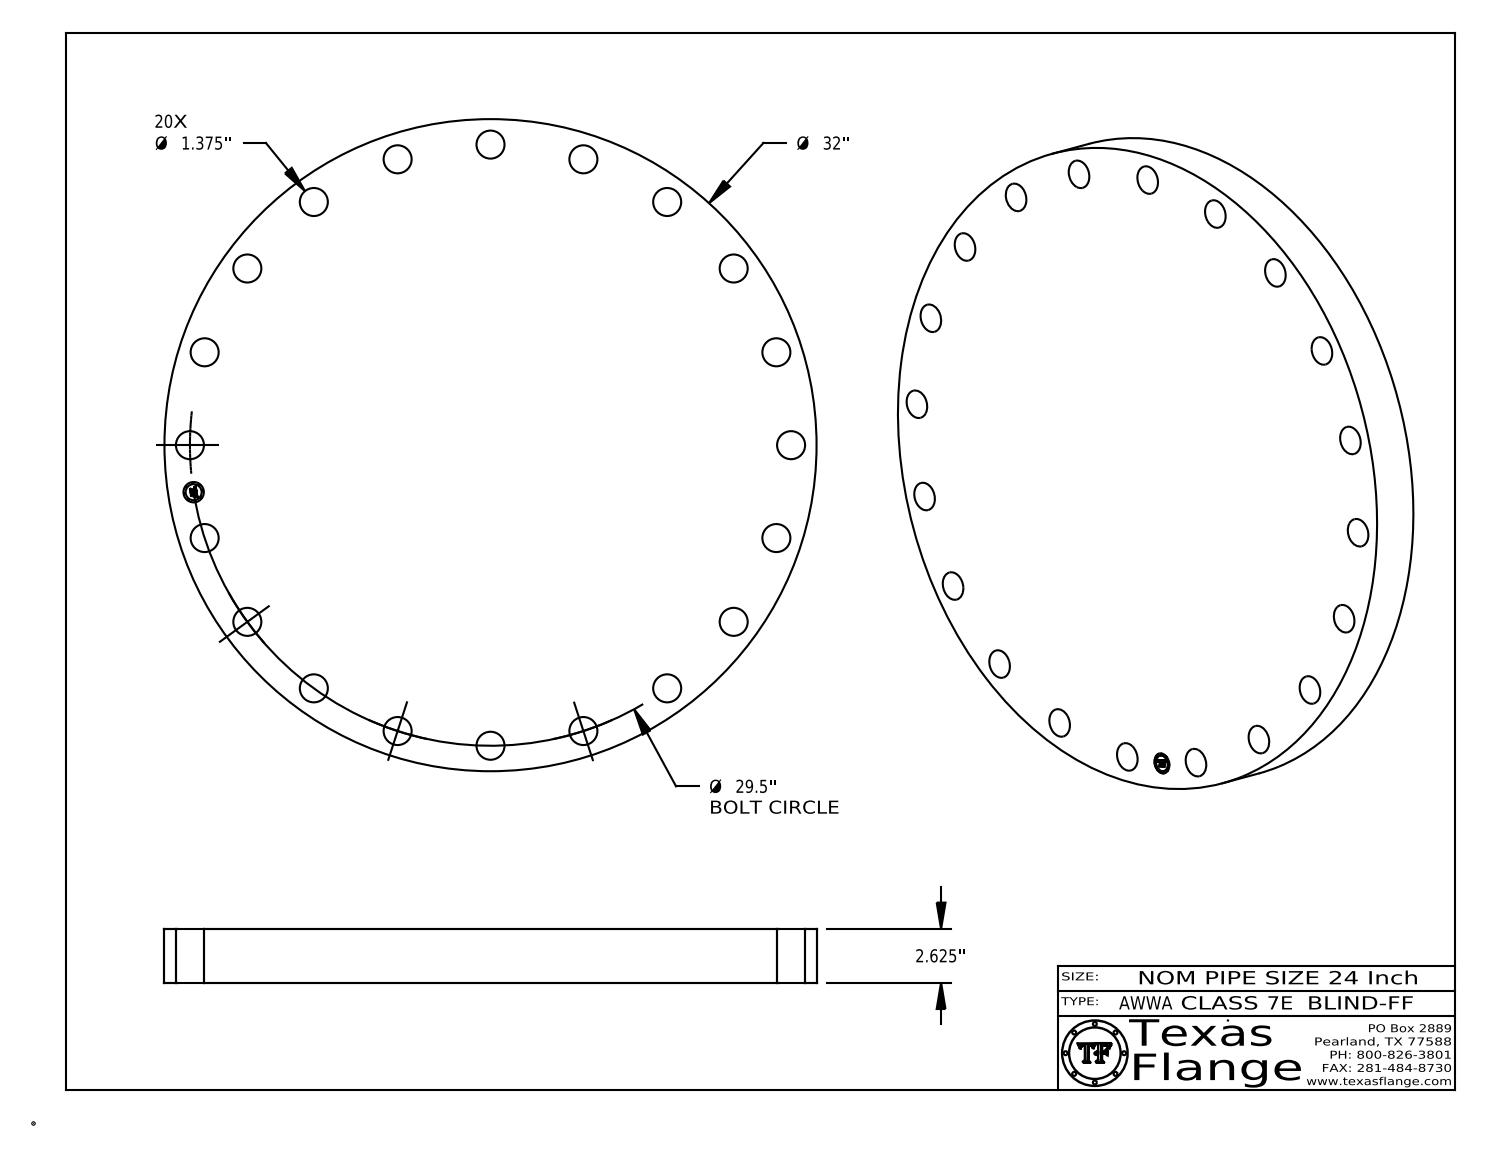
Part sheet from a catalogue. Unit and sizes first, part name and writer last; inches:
Units: inches
Overall size (bounding box): 32 × 32 × 2.625
Round holes (diameter × count): ⌀1.375 ×20, ⌀1 ×1
Round bosses / shafts (diameter × count): ⌀0.061 ×8, ⌀32 ×1, ⌀0.788 ×1
Main face-to-face distances: 2.625, 0.015, 2.61, 0.298, 0.293, 0.054, 0.193, 0.248, 0.044, 0.15
Hole centre spacings: 29.137, 4.615, 17.34, 20.859, 23.866, 26.285, 9.116, 13.393
Volume: 2 033 in³ · Surface area: 2 040 in²
Bodies: 1 solid, 429 faces (367 planar, 62 cylindrical, 0 other)
Part name (STEP PRODUCT): AWWA Class 7E-BLIND-FF
STEP written by: CATIA V5 STEP AP214 (AUTOMOTIVE_DESIGN)
